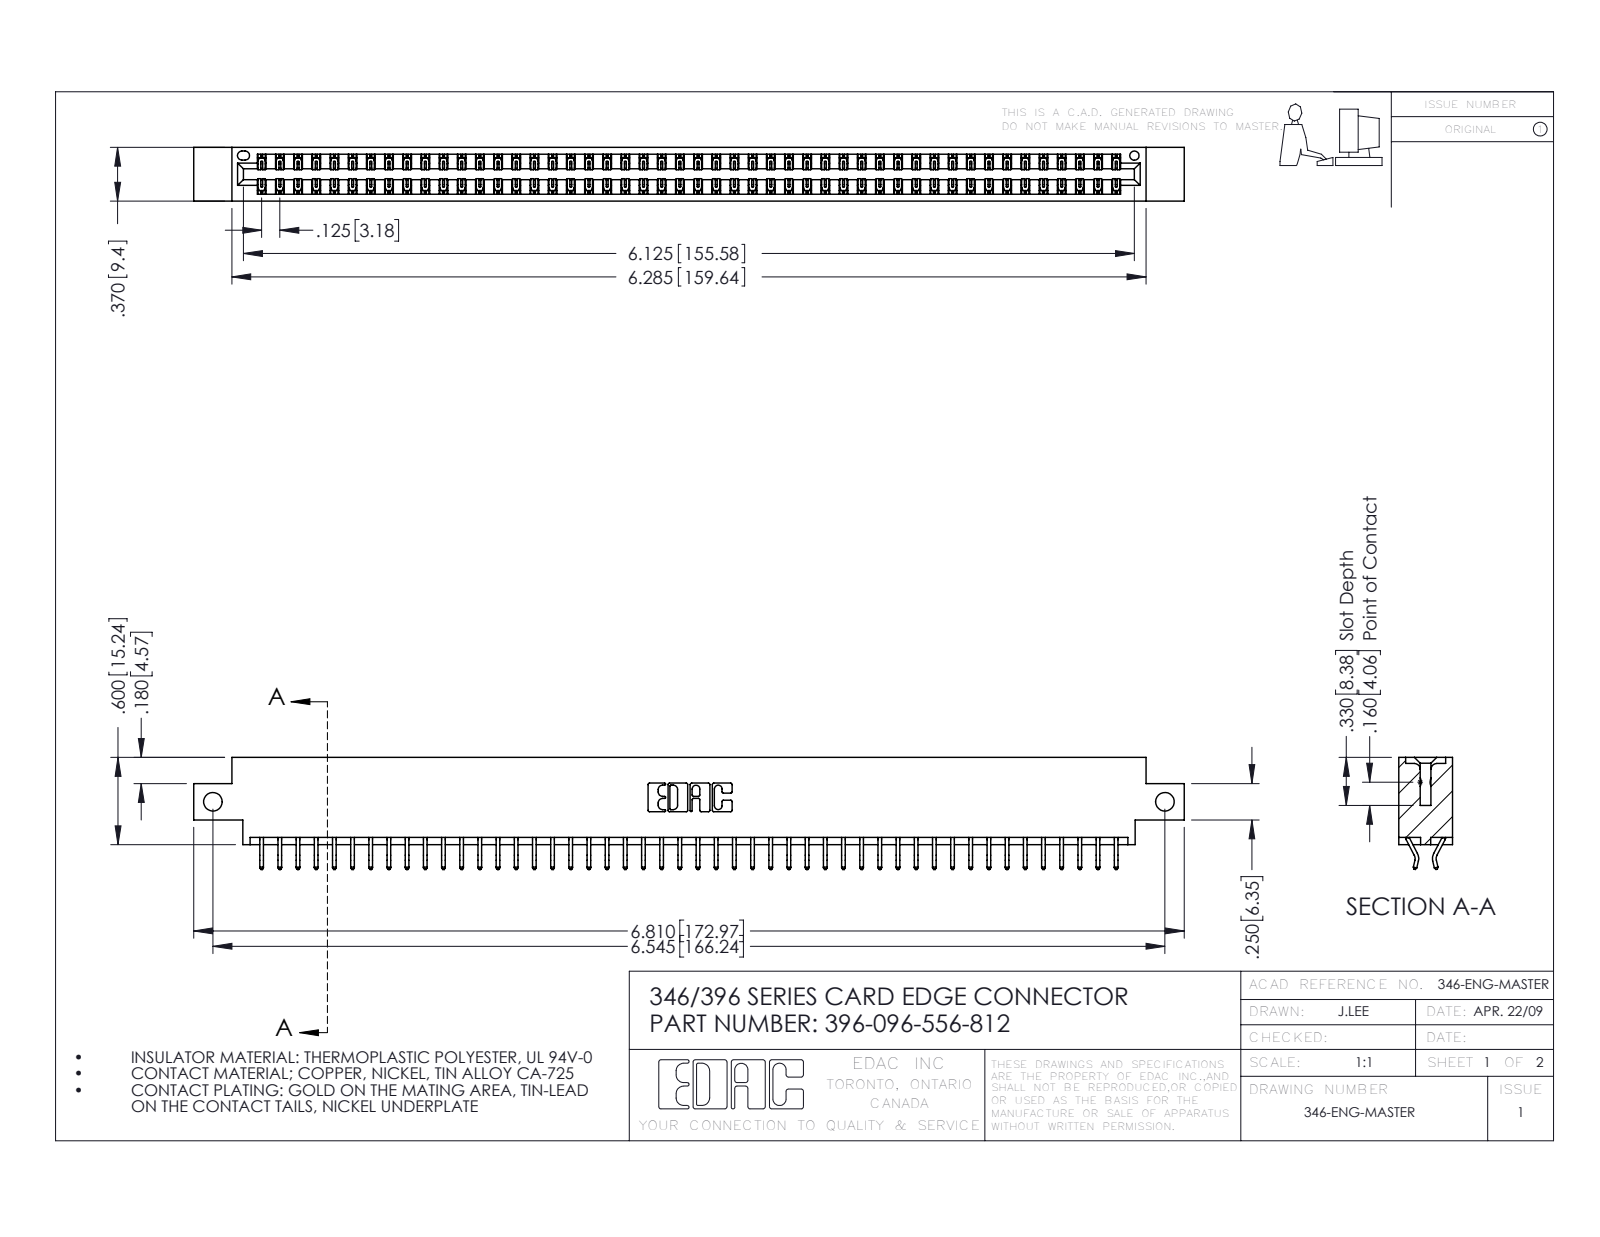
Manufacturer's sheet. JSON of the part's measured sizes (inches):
{"part_name": "345-292-001_556 Tail; 396-096-556-812; 346 Part_0.170 Offset - Side Mount", "step_written_by": "SolidWorks 2016 (CONFIG_CONTROL_DESIGN)", "units": "inches", "bodies": {"solids": 97, "faces": 5694, "planar": 3824, "cylindrical": 1870, "other": 0}, "overall_size": [6.81, 0.77, 0.37], "volume_in3": 1.017, "surface_area_in2": 35.59, "round_holes": [[0.128, 2], [0.064, 1]], "partial_cylinders_radius": [[0.006, 144], [0.01, 22], [0.007, 6], [0.031, 6], [0.026, 3], [0.01, 2], [0.014, 2], [0.022, 2]], "face_to_face_distances": [0.048, 0.322, 0.37, 0.25, 0.025, 0.072, 0.298, 0.275, 0.148, 0.222], "hole_center_spacings": [6.545]}
